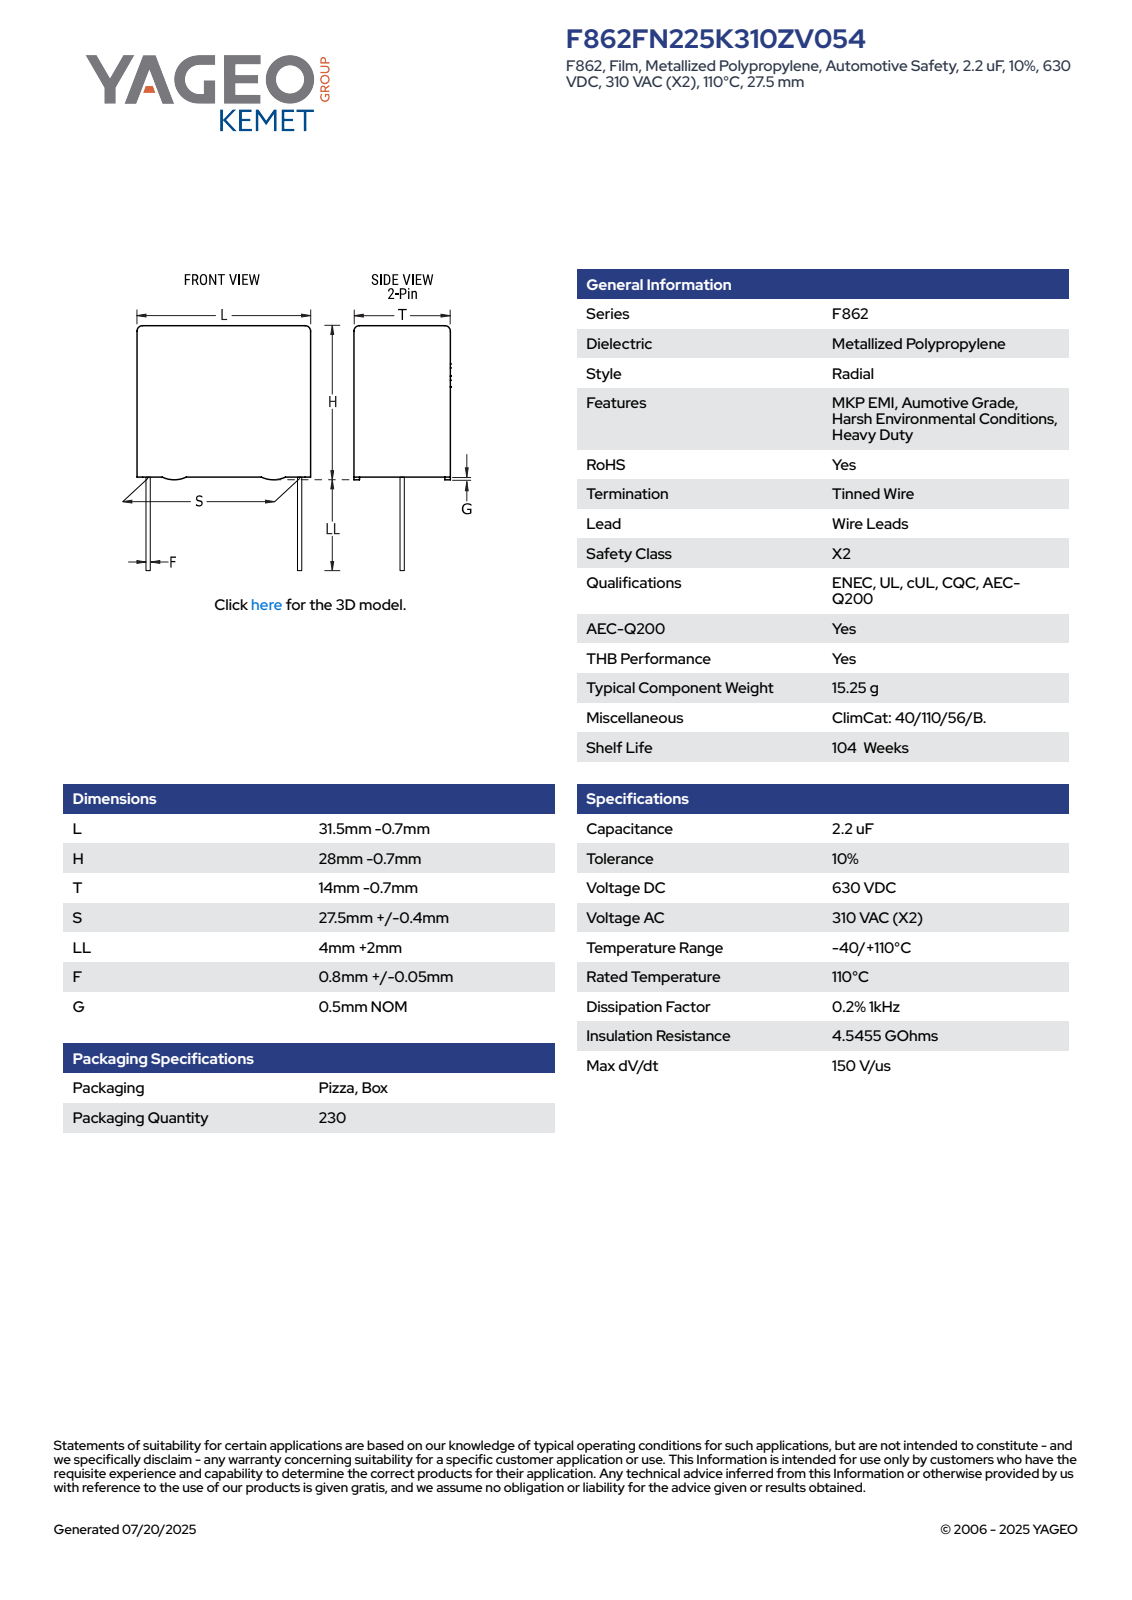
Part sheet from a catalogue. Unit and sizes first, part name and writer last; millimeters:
Units: millimetres
Overall size (bounding box): 33.3 × 30.8 × 13.3
Round bosses / shafts (diameter × count): ⌀0.85 ×2
Partial cylindrical surfaces — rounded edges, fillets, slot ends (radius × count): R0.5 ×4
Main face-to-face distances: 13.3, 26.8, 30.8, 13.31, 0.5, 27.3, 0.76, 12.54, 0.77, 11.78
Volume: 10 989 mm³ · Surface area: 3 323 mm²
Bodies: 4 solids, 89 faces (81 planar, 8 cylindrical, 0 other)
Part name (STEP PRODUCT): CFR_RBG_31.5X28X14_L30.8H27.3T13.3S27.5LL6F0.85G0.5
STEP written by: SolidWorks 2014 (AUTOMOTIVE_DESIGN)
